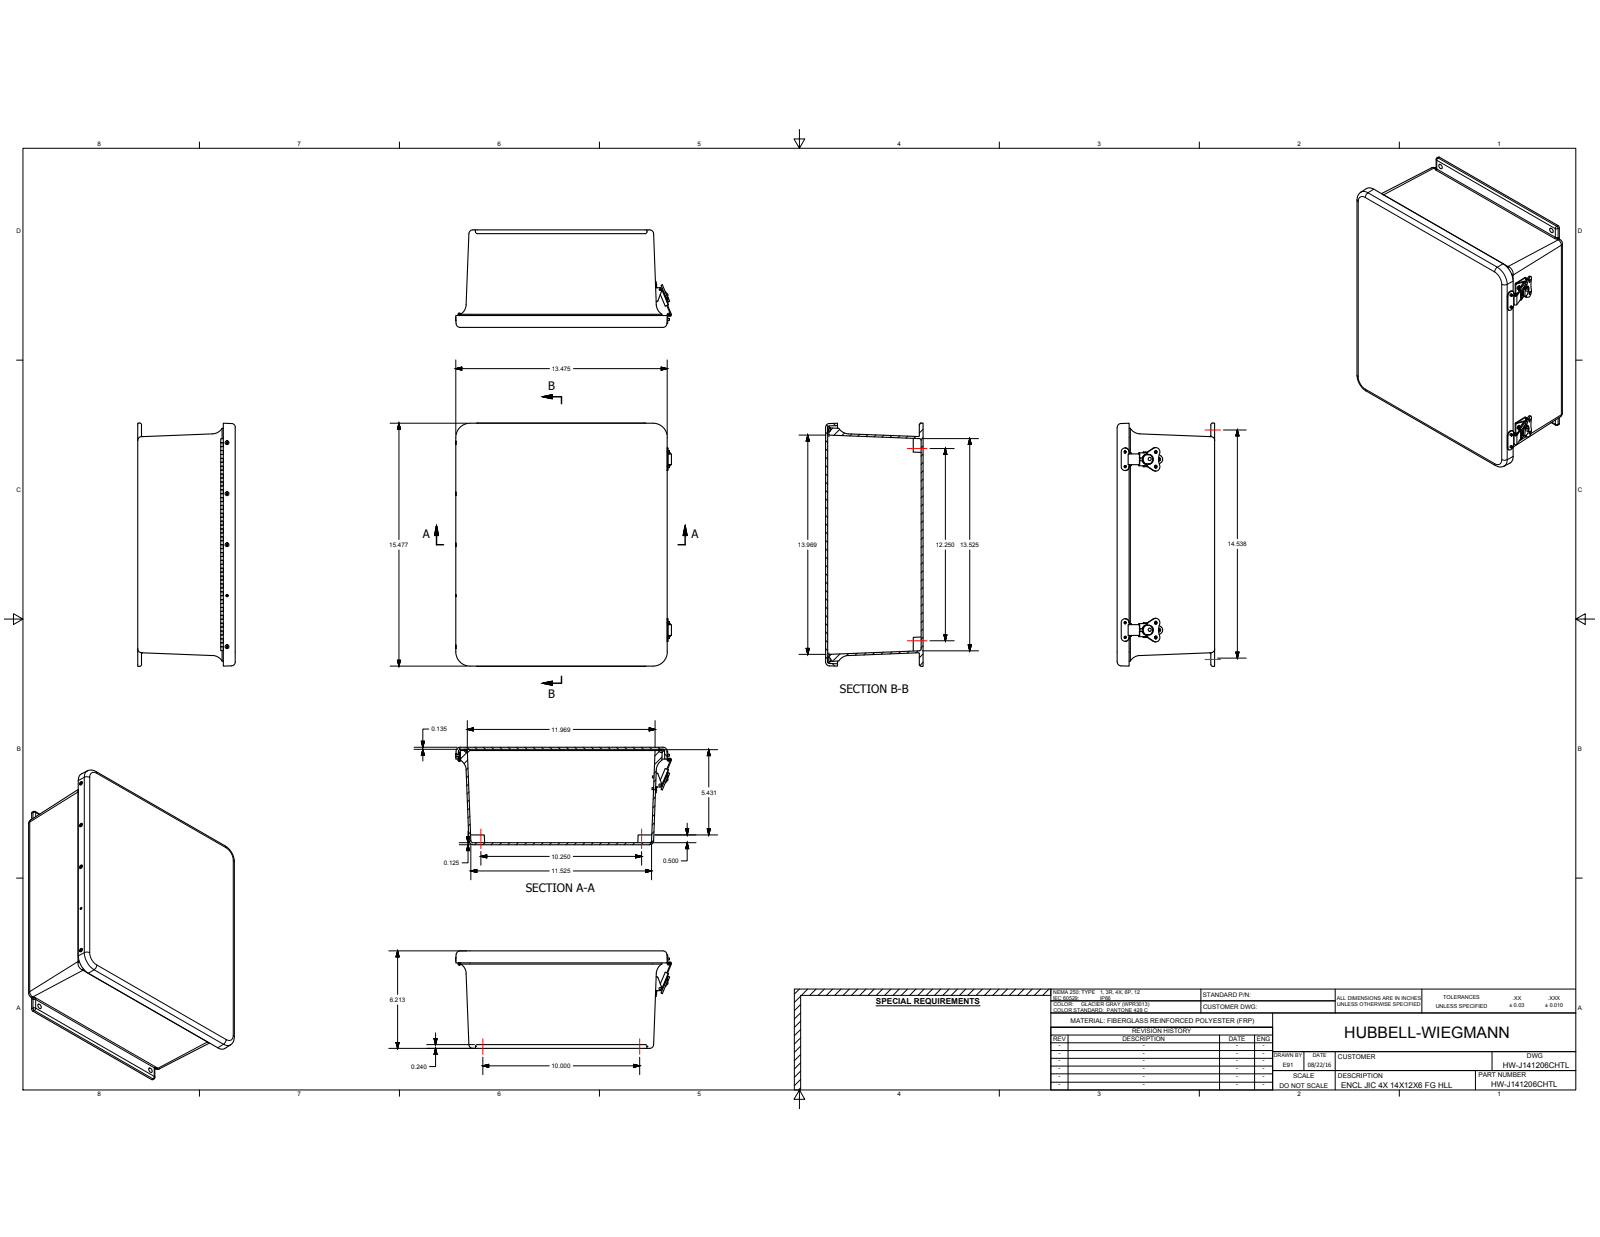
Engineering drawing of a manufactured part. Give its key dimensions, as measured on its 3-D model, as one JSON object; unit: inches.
{"part_name": "HW-J1412CHTL; WP1412H&LBOX; WP1412HLU; WP1412H&LCVR (+8 more)", "step_written_by": "Autodesk Inventor 2017 (CONFIG_CONTROL_DESIGN)", "units": "inches", "bodies": {"solids": 44, "faces": 1050, "planar": 503, "cylindrical": 429, "other": 118}, "overall_size": [15.5, 13.683, 6.213], "volume_in3": 113.8, "surface_area_in2": 1606, "round_holes": [[0.14, 20], [0.104, 18], [0.131, 10], [0.152, 8], [0.13, 4], [0.133, 4], [0.187, 4], [0.218, 4], [0.312, 4], [0.135, 2], [0.189, 2], [0.191, 2]], "round_bosses_or_shafts": [[0.125, 18], [0.66, 2], [0.582, 2], [0.525, 2], [0.286, 2], [0.213, 2], [0.18, 2], [0.125, 2]], "partial_cylinders_radius": [[0.125, 17], [0.015, 16], [0.06, 13], [0.25, 10], [0.011, 8], [0.02, 8], [0.055, 8], [0.07, 8]], "face_to_face_distances": [0.125, 0.135, 6.213, 6.078, 6.087, 5.953, 0.125, 0.33, 0.152, 0.213], "hole_center_spacings": [3.25, 6.5, 9.75, 10.882, 10.881, 0.937, 0.013, 0.25]}
